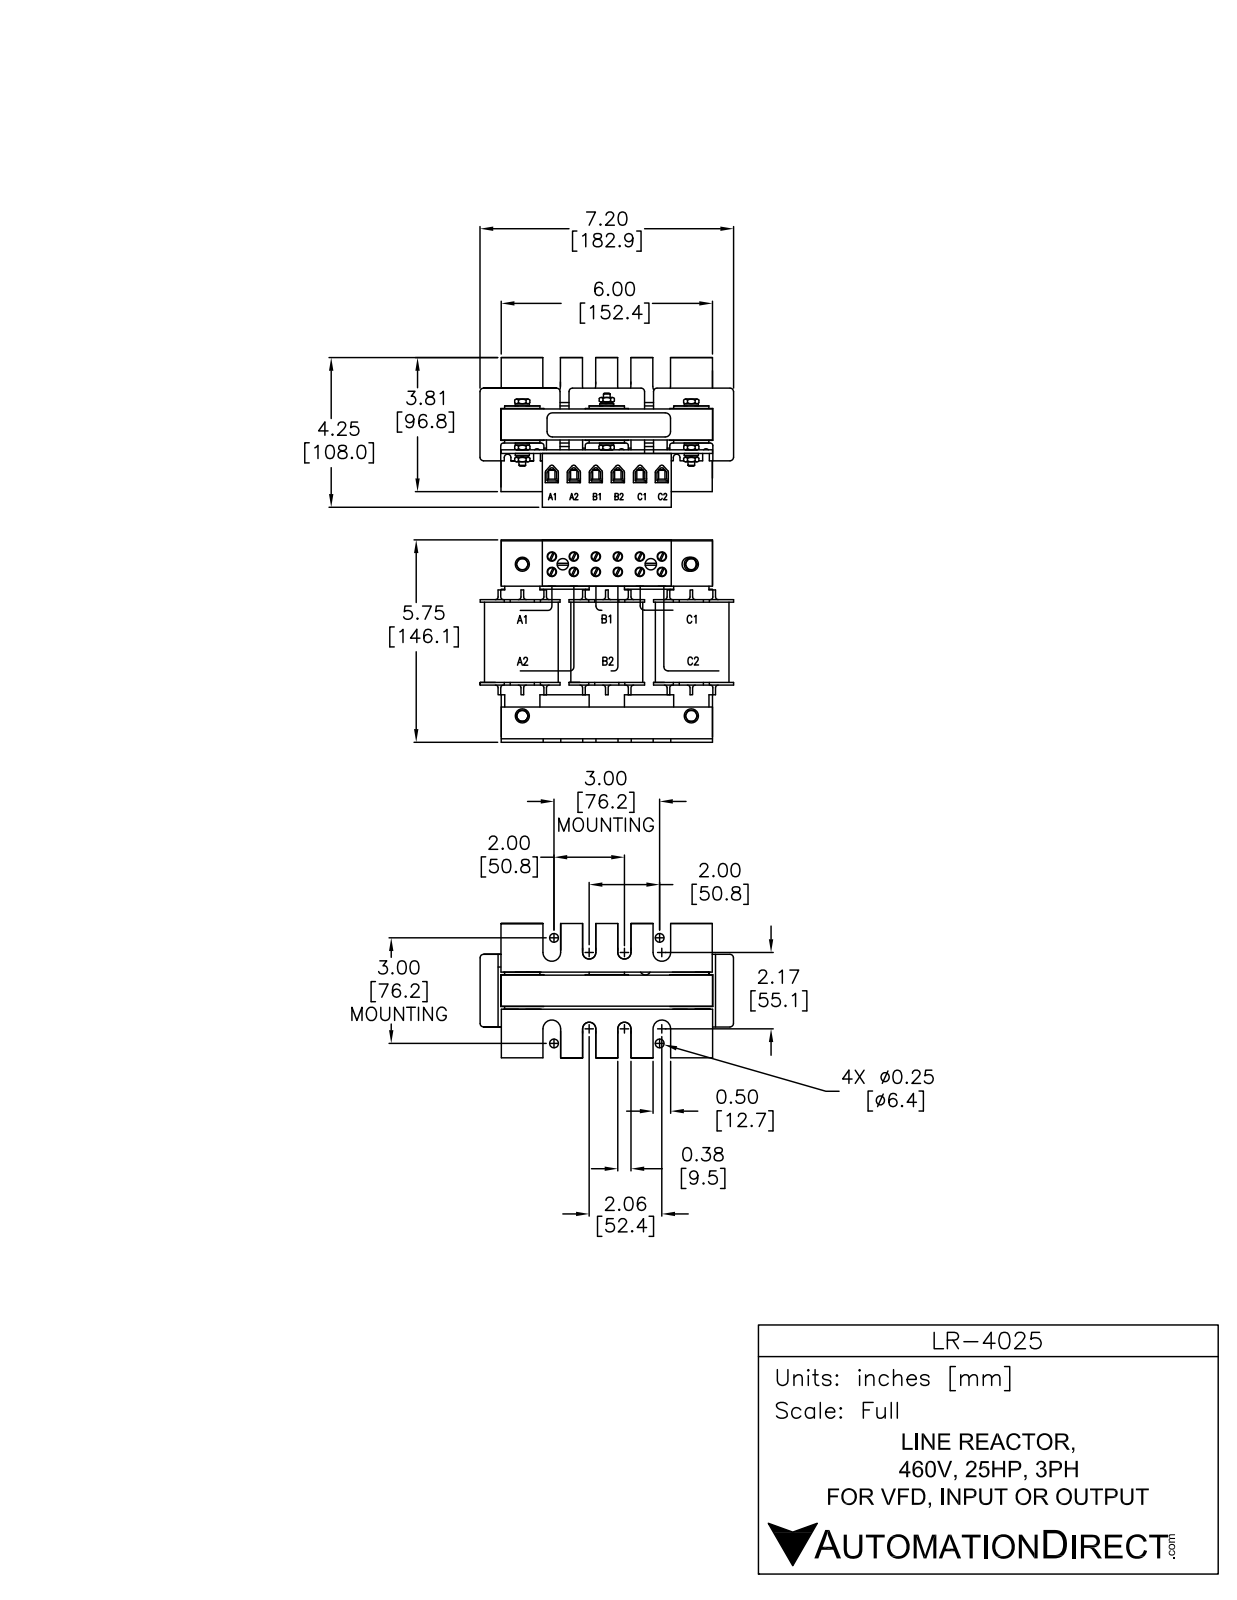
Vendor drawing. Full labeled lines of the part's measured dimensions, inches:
Part name (STEP PRODUCT): LR-4025
STEP written by: SolidWorks 2011 (AUTOMOTIVE_DESIGN)
Units: inches
Bodies: 34 solids, 1041 faces (767 planar, 242 cylindrical, 32 other)
Overall size (bounding box): 7.008 × 5.619 × 3.907
Volume: 51.71 in³ · Surface area: 302.9 in²
Round holes (diameter × count): ⌀0.276 ×12, ⌀0.305 ×5
Round bosses / shafts (diameter × count): ⌀0.472 ×5, ⌀0.413 ×5, ⌀0.305 ×2, ⌀0.183 ×2, ⌀0.184 ×1, ⌀0.183 ×1, ⌀0.183 ×1
Partial cylindrical surfaces — rounded edges, fillets, slot ends (radius × count): R0.106 ×24, R0.197 ×12, R0.276 ×12, R0.089 ×6, R0.059 ×4, R0.177 ×4, R0.246 ×4, R0.128 ×2
Main face-to-face distances: 0.079, 0.364, 2.441, 1.329, 1.407, 0.108, 0.344, 0.266, 0.443, 0.187
Hole centre spacings: 0.63, 1.26, 0.376, 0.394, 0.77, 0.96, 0.981, 1.335
